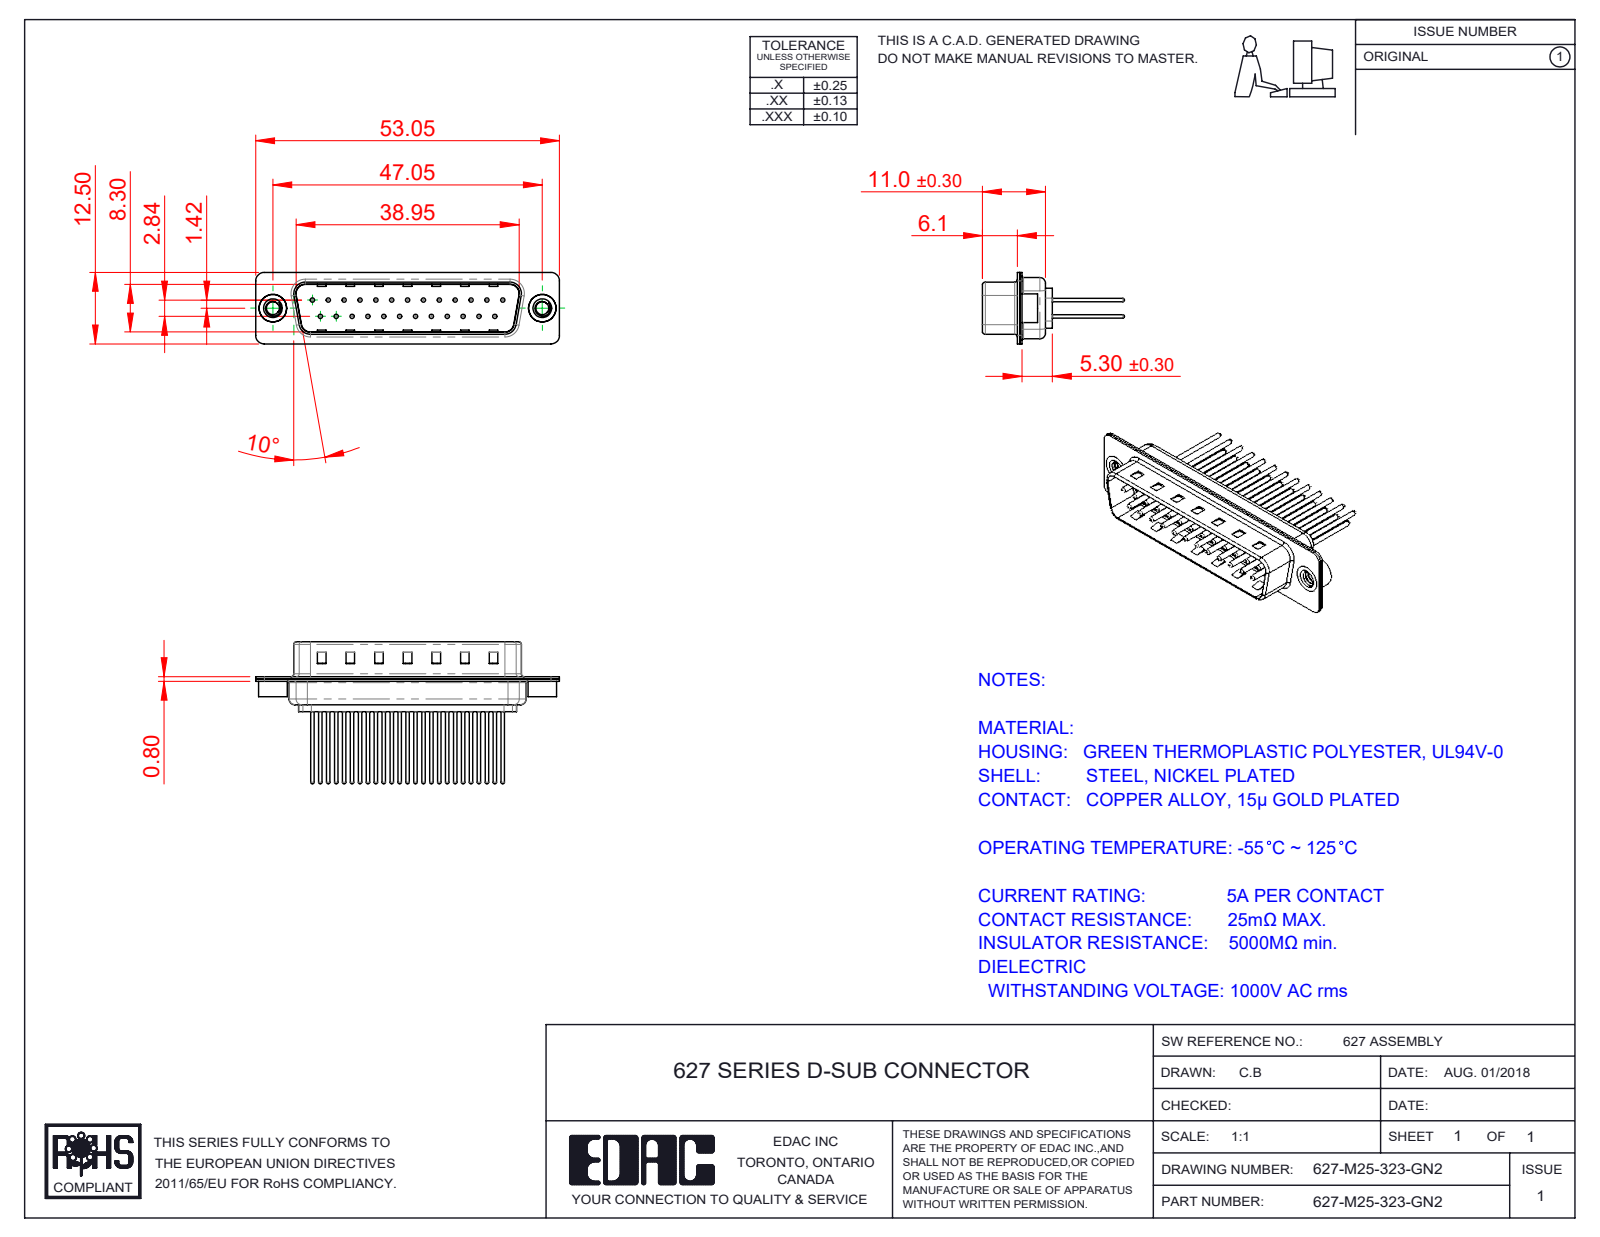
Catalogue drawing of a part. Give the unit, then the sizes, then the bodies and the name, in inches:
Units: inches
Overall size (bounding box): 2.089 × 0.975 × 0.492
Round holes (diameter × count): ⌀0.03 ×25, ⌀0.063 ×25, ⌀0.079 ×25, ⌀0.089 ×2, ⌀0.157 ×2, ⌀0.189 ×2
Round bosses / shafts (diameter × count): ⌀0.059 ×25, ⌀0.024 ×25, ⌀0.197 ×2, ⌀0.193 ×2
Partial cylindrical surfaces — rounded edges, fillets, slot ends (radius × count): R0.059 ×16, R0.079 ×12, R0.02 ×8, R0.063 ×8, R0.01 ×4, R0.024 ×4, R0.026 ×4, R0.035 ×4
Main face-to-face distances: 0.016, 0.031, 0.374, 0.358, 0.343, 0.39, 0.047, 0.24, 0.224, 0.03
Hole centre spacings: 0.124, 0.109, 0.218, 0.327, 0.436, 0.545, 0.654, 0.198
Volume: 0.169 in³ · Surface area: 11.11 in²
Bodies: 30 solids, 1301 faces (346 planar, 487 cylindrical, 468 other)
Part name (STEP PRODUCT): 627-M25-323-GN2; 627M Shell Rear_25 Contacts; 627M Housing_25 Contacts; 627M Contact Row 1_23 (+3 more)
STEP written by: SolidWorks 2020 (CONFIG_CONTROL_DESIGN)
